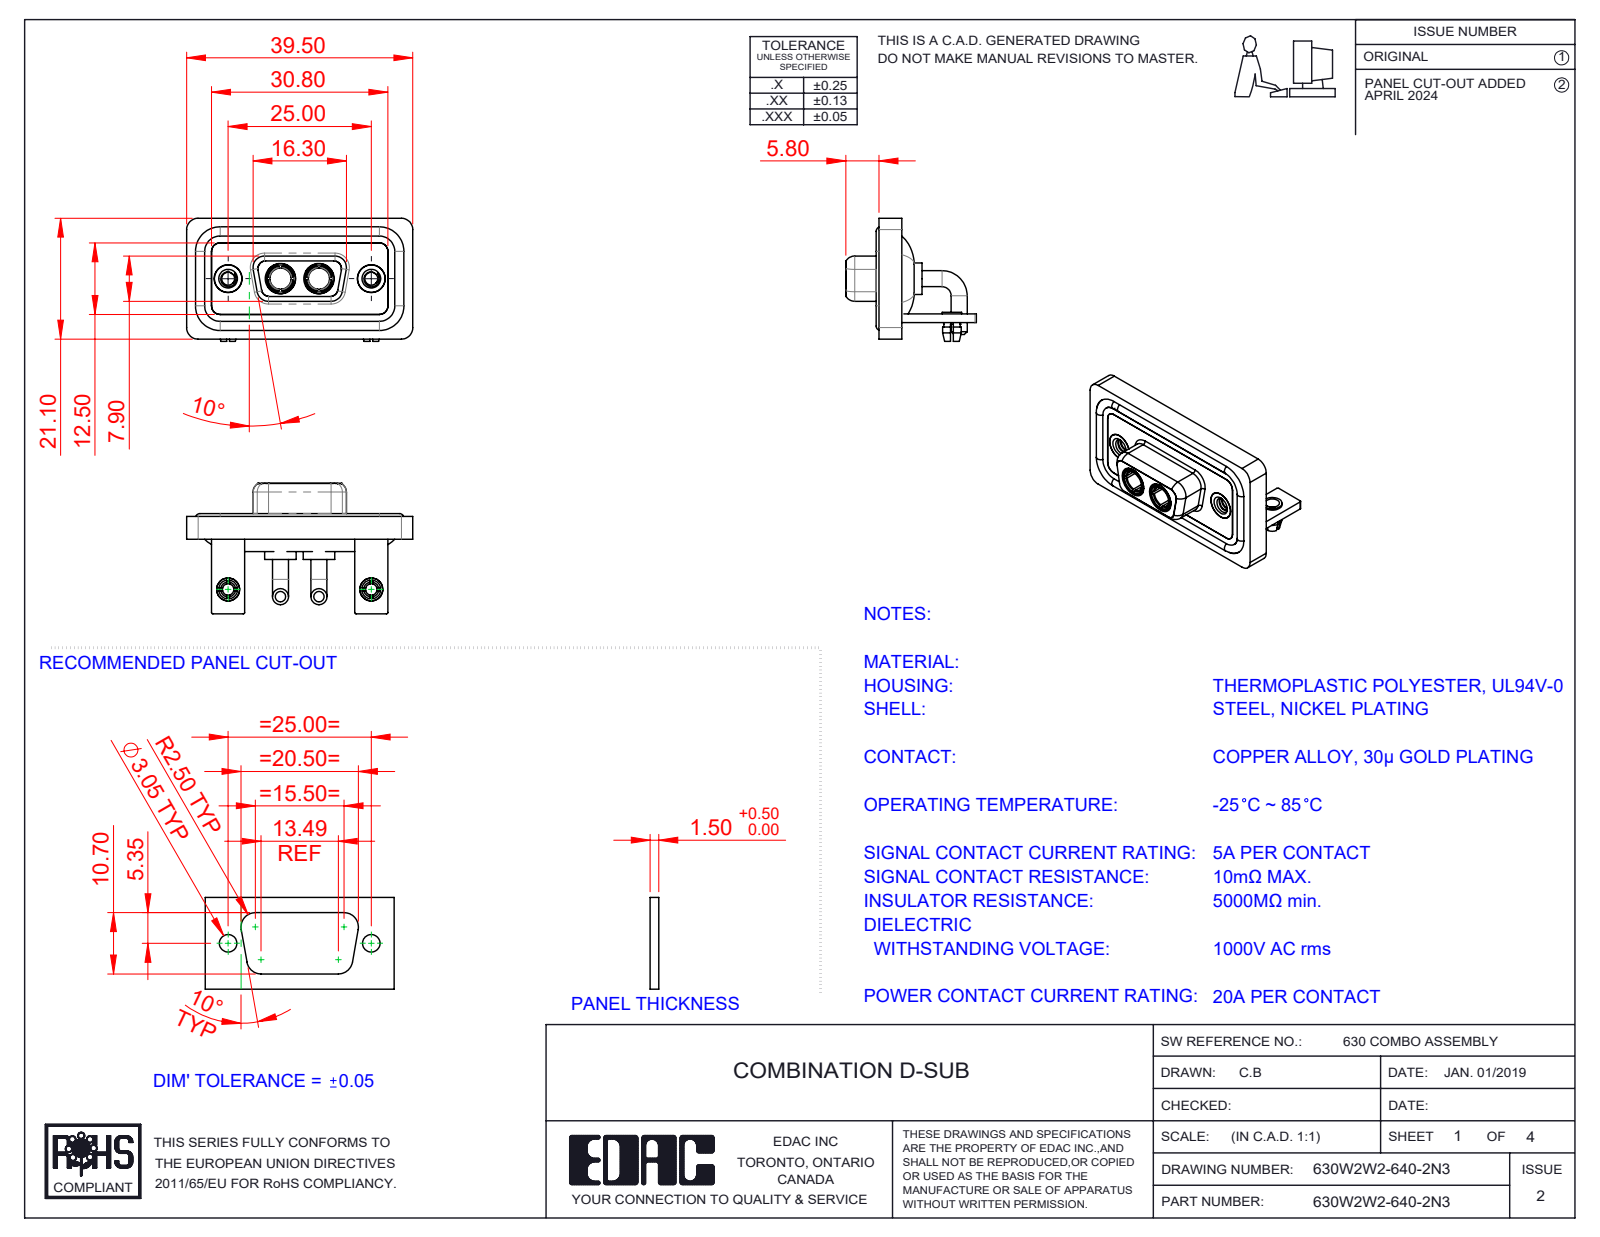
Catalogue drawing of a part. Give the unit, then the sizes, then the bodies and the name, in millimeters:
Units: millimetres
Overall size (bounding box): 39.5 × 22.8 × 21.5
Round holes (diameter × count): ⌀4.85 ×4, ⌀2 ×2, ⌀2.26 ×2, ⌀2.5 ×2, ⌀3.2 ×2, ⌀3.7 ×2, ⌀4 ×2, ⌀4.05 ×2, ⌀5 ×2, ⌀5.3 ×2
Round bosses / shafts (diameter × count): ⌀2.8 ×4, ⌀1.6 ×4, ⌀5.5 ×2, ⌀5.2 ×2, ⌀4.96 ×2, ⌀4.95 ×2, ⌀4.8 ×2, ⌀4.75 ×2
Partial cylindrical surfaces — rounded edges, fillets, slot ends (radius × count): R2 ×19, R1.5 ×18, R0.25 ×16, R1.35 ×8, R1.6 ×8, R0.5 ×5, R0.6 ×4, R0.65 ×4
Main face-to-face distances: 0.4, 2.9, 1.5, 1.8, 1.1, 3.7, 0.8, 2.5, 1.6, 3.1
Hole centre spacings: 9.14, 15.86, 25, 6.72
Volume: 5 219 mm³ · Surface area: 8 732 mm²
Bodies: 15 solids, 682 faces (231 planar, 294 cylindrical, 157 other)
Part name (STEP PRODUCT): 630W2W2-640-2N3; Power Socket_20A RA; 630Combo Shell Rear_09 Contacts; 630Combo Threaded Rivet_2 (+5 more)
STEP written by: SolidWorks 2023 (CONFIG_CONTROL_DESIGN)
